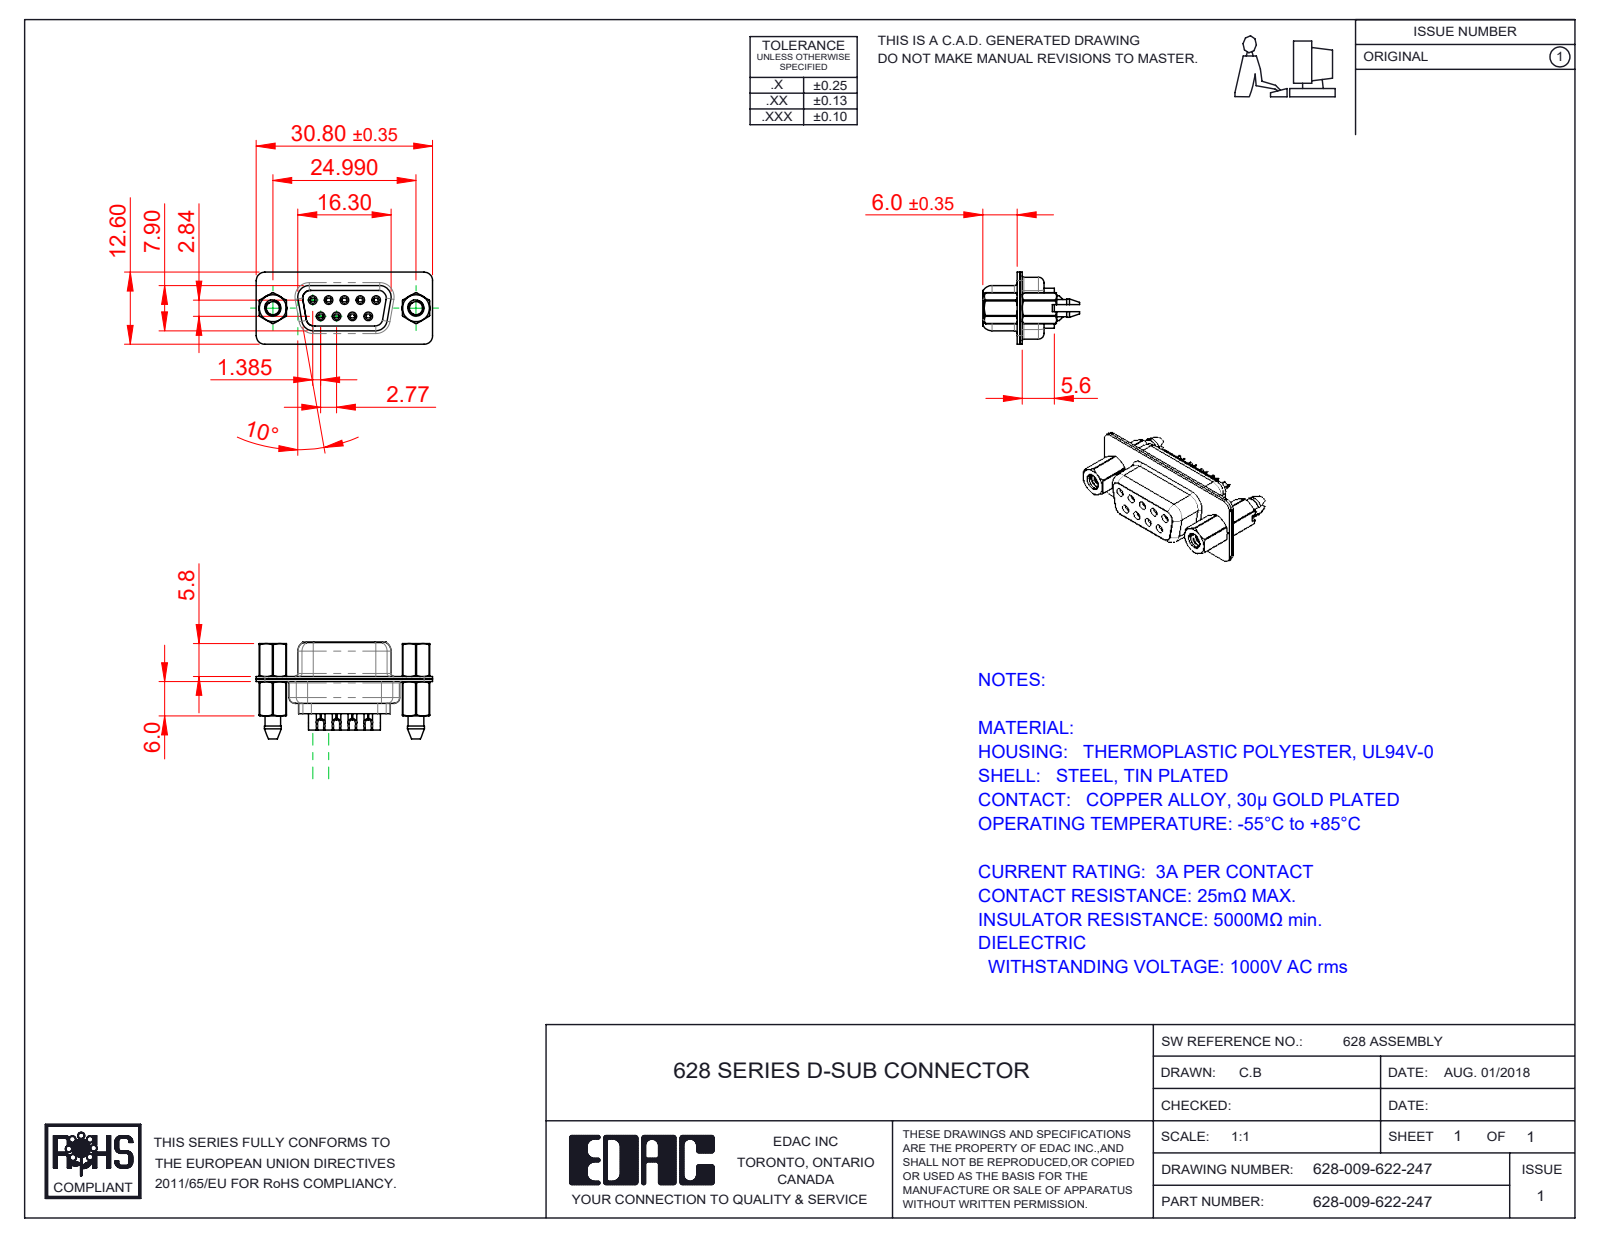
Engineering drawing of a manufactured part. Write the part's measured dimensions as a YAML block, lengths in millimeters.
part_name: "628 Shell Rear_09 Contacts; 628 Shell Front_09 Contacts; 628-009-622-247; 628 4-40 Hex Standoff (+4 more)"
step_written_by: "SolidWorks 2020 (CONFIG_CONTROL_DESIGN)"
units: millimeters
bodies: {solids: 16, faces: 1280, planar: 310, cylindrical: 466, other: 504}
overall_size: [30.8, 16.9, 12.6]
volume: 2088
surface_area: 5299
round_holes:
  - {diameter: 0.8, count: 9}
  - {diameter: 0.9, count: 9}
  - {diameter: 1.1, count: 9}
  - {diameter: 1.6, count: 9}
  - {diameter: 1.7, count: 5}
  - {diameter: 2.26, count: 2}
  - {diameter: 2.29, count: 2}
  - {diameter: 4, count: 2}
  - {diameter: 4.05, count: 2}
  - {diameter: 4.85, count: 2}
round_bosses_or_shafts:
  - {diameter: 2, count: 9}
  - {diameter: 1.5, count: 9}
  - {diameter: 1.2, count: 9}
  - {diameter: 4.95, count: 2}
  - {diameter: 4.8, count: 2}
  - {diameter: 2.79, count: 2}
partial_cylinders:
  - {radius: 1.5, count: 19}
  - {radius: 2, count: 12}
  - {radius: 0.28, count: 9}
  - {radius: 1, count: 6}
  - {radius: 1.35, count: 6}
  - {radius: 1.6, count: 6}
  - {radius: 0.25, count: 4}
  - {radius: 0.5, count: 4}
face_to_face_distances: [0.45, 0.4, 0.9, 1.9, 8.5, 6.6, 1.4, 12.5, 4.76, 0.5]
hole_center_spacings: [3.16, 2.77, 5.54, 5.03, 5.04, 8.31, 7.48, 7.49]
